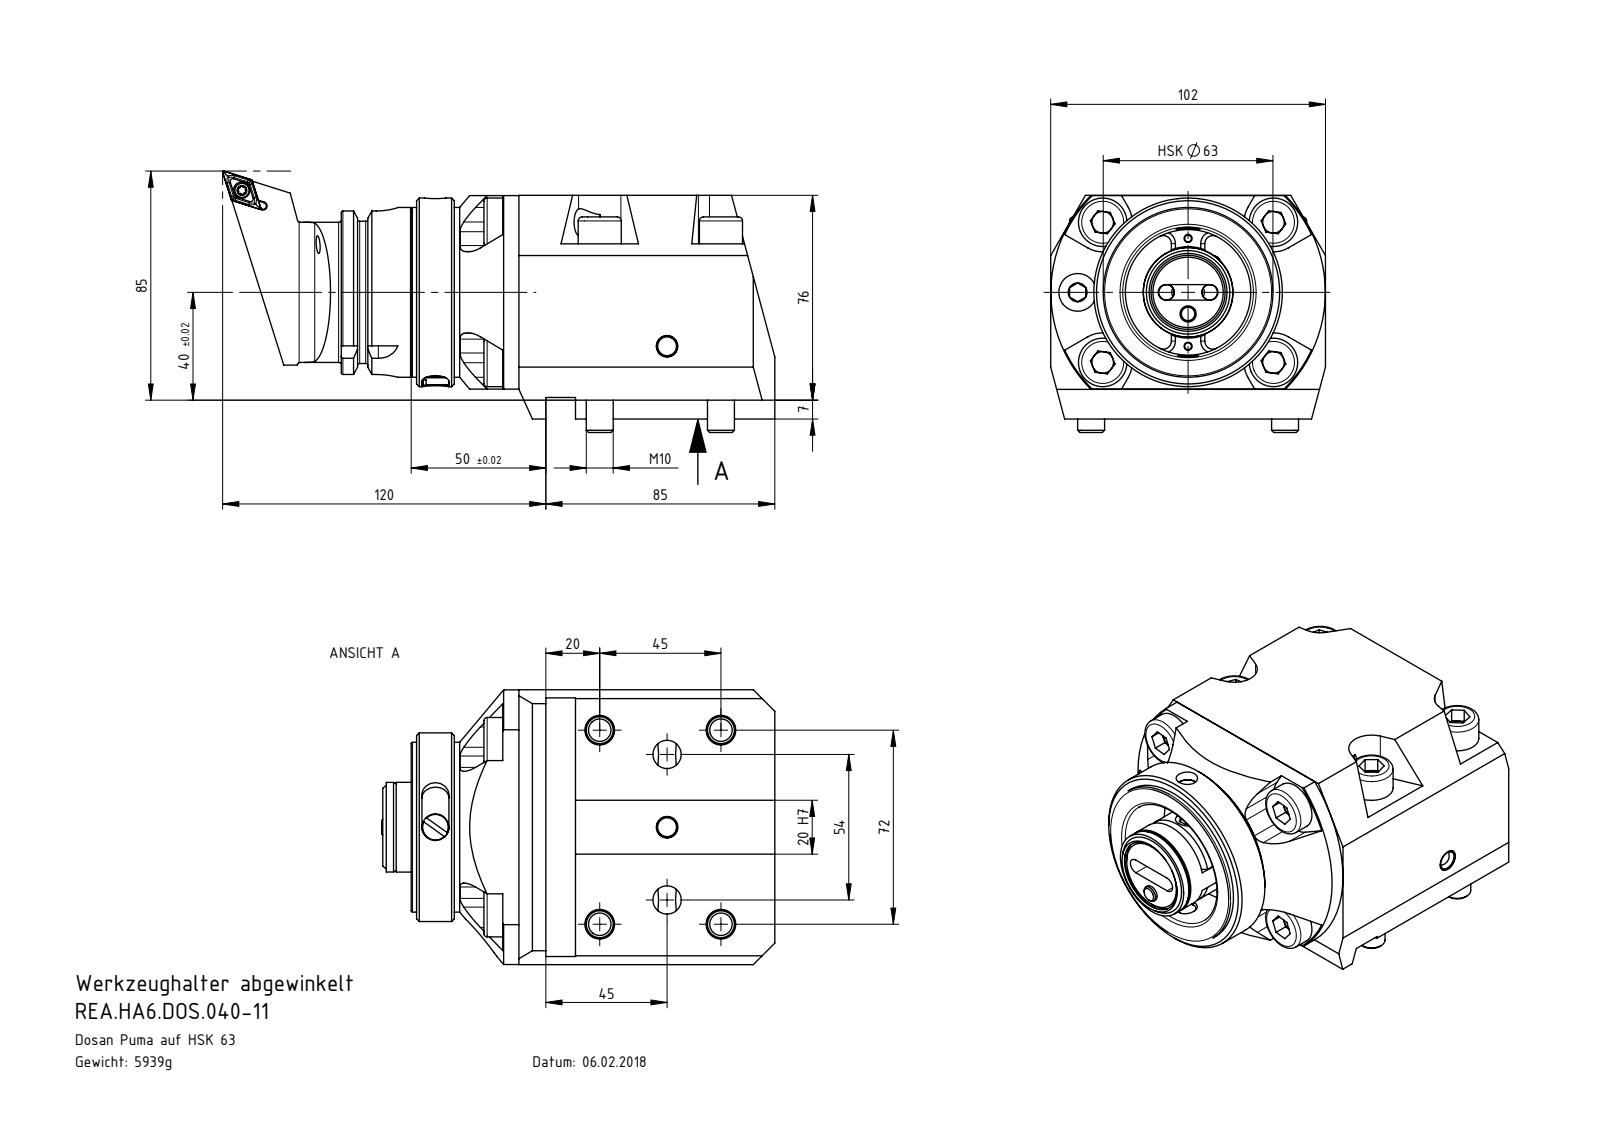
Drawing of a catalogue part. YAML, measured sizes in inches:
part_name: "DIN 3771 - 17x2; Spindel6; HA6-ER1.001.000; REA.HA6.DOS.040-11 (+8 more)"
step_written_by: "SolidWorks 2017 (AUTOMOTIVE_DESIGN)"
units: inches
bodies: {solids: 28, faces: 587, planar: 290, cylindrical: 152, other: 145}
overall_size: [5.746, 4.016, 3.465]
volume: 47.7
surface_area: 236.7
round_holes:
  - {diameter: 0.268, count: 4}
  - {diameter: 0.402, count: 4}
  - {diameter: 0.433, count: 4}
  - {diameter: 0.512, count: 4}
  - {diameter: 0.098, count: 2}
  - {diameter: 0.226, count: 2}
  - {diameter: 0.228, count: 2}
  - {diameter: 0.276, count: 2}
  - {diameter: 0.315, count: 2}
  - {diameter: 0.413, count: 2}
  - {diameter: 0.157, count: 1}
  - {diameter: 0.197, count: 1}
round_bosses_or_shafts:
  - {diameter: 0.63, count: 5}
  - {diameter: 0.709, count: 4}
  - {diameter: 0.472, count: 4}
  - {diameter: 0.394, count: 4}
  - {diameter: 0.315, count: 2}
  - {diameter: 2.756, count: 1}
  - {diameter: 2.48, count: 1}
  - {diameter: 2.461, count: 1}
partial_cylinders:
  - {radius: 0.118, count: 12}
  - {radius: 0.197, count: 8}
  - {radius: 0.433, count: 5}
  - {radius: 0.114, count: 4}
  - {radius: 0.335, count: 4}
  - {radius: 0.039, count: 2}
  - {radius: 0.113, count: 2}
  - {radius: 0.159, count: 1}
face_to_face_distances: [2.992, 0.945, 0.157, 0.787, 4.016, 0.551, 2.953, 0.394, 0.315, 0.276]
hole_center_spacings: [1.614, 0.848, 1.27, 1.385, 1.869, 2.199, 0.315, 0.445]
